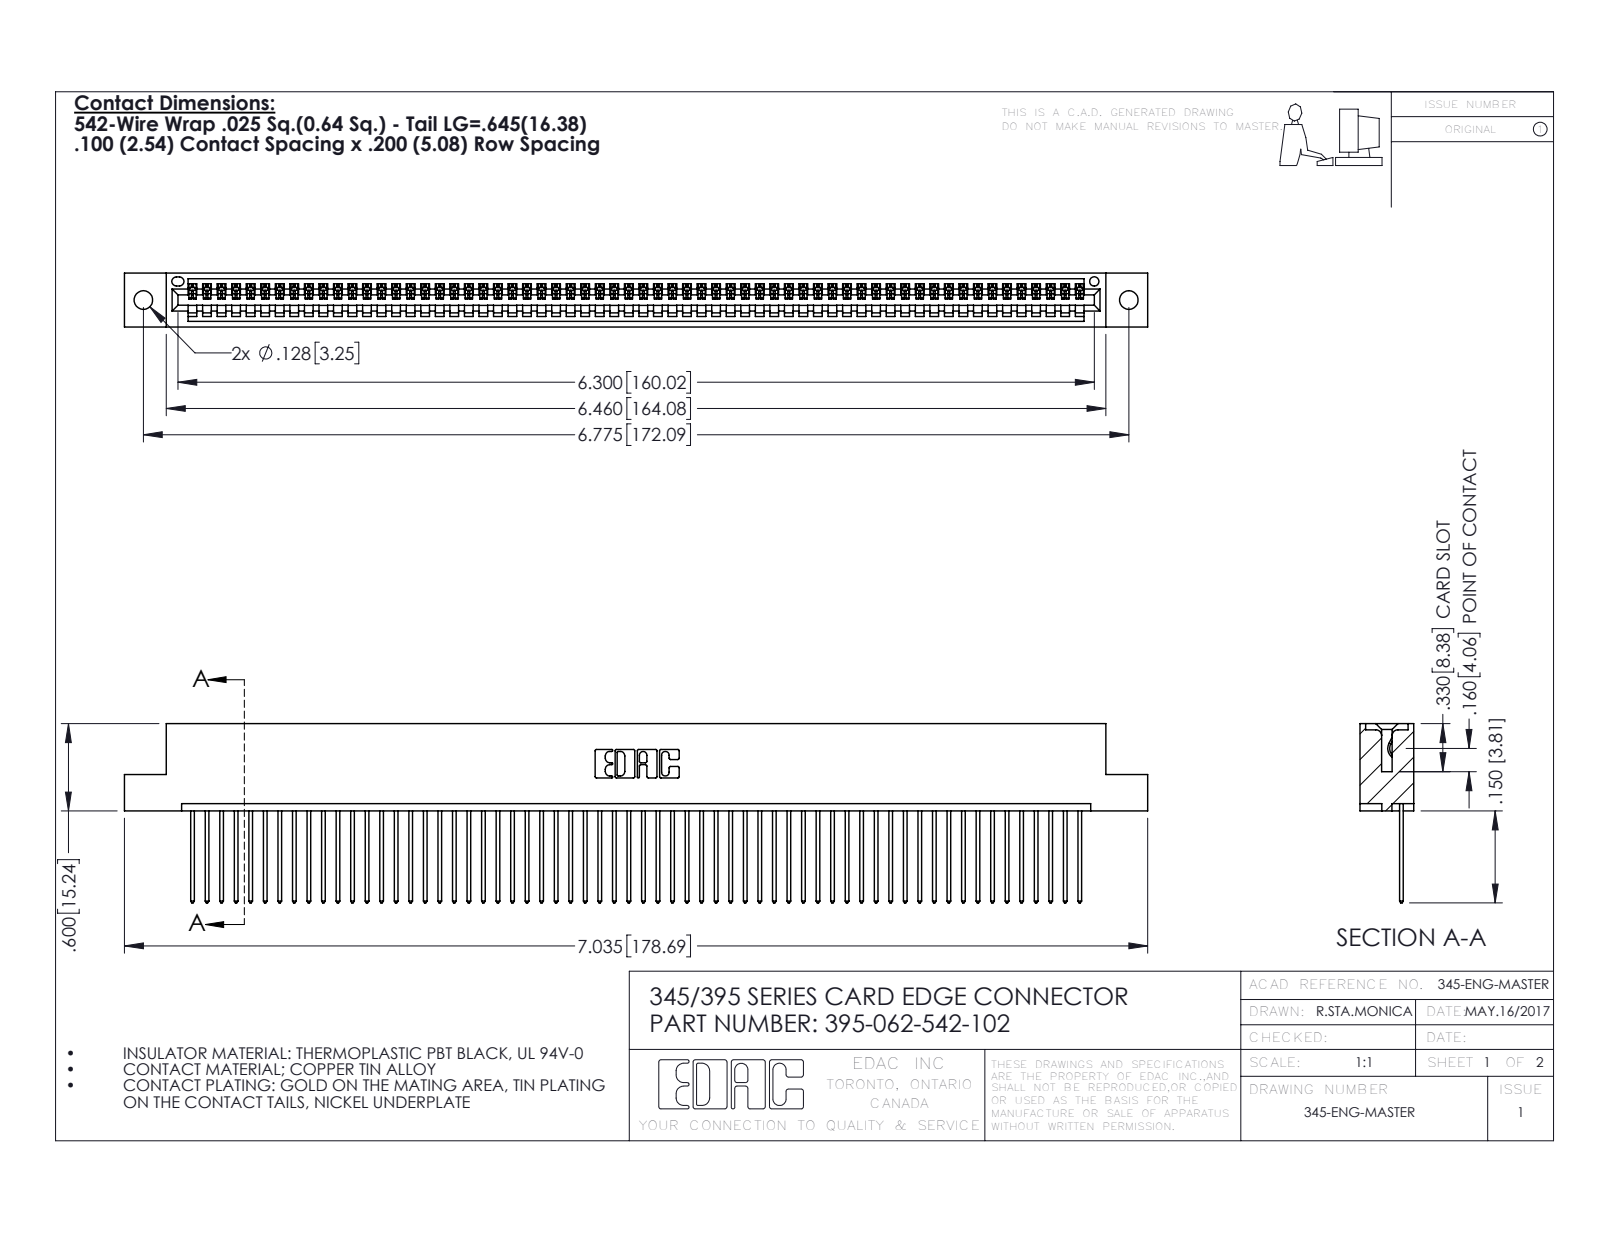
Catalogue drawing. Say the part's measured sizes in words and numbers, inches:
The part is named "395-062-542-102; 345-292-001_345-293-142; 345 Part_Flush Mounting Lugs - 0.128 Dia". Its 3-D file was written by "SolidWorks 2016 (CONFIG_CONTROL_DESIGN)". It is 63 solids with 3722 faces: 2560 planar, 1162 cylindrical and 0 other. Overall it measures 7.035 by 1.232 by 0.37 inches. Its volume is 1.052 cubic inches and its surface area 36.86 square inches. Round holes: 2 of diameter 0.128, 1 of diameter 0.064. Partial cylindrical surfaces (rounded edges, fillets, slot ends): 124 of radius 0.006, 124 of radius 0.01, 22 of radius 0.01, 6 of radius 0.007, 6 of radius 0.031, 3 of radius 0.026, 2 of radius 0.031, 2 of radius 0.04. The main face-to-face distances are 0.072, 0.298, 0.098, 0.272, 0.025, 0.37, 0.2, 0.225, 0.149, 0.072. The hole center spacings are 0.27, 6.539, 6.775.
